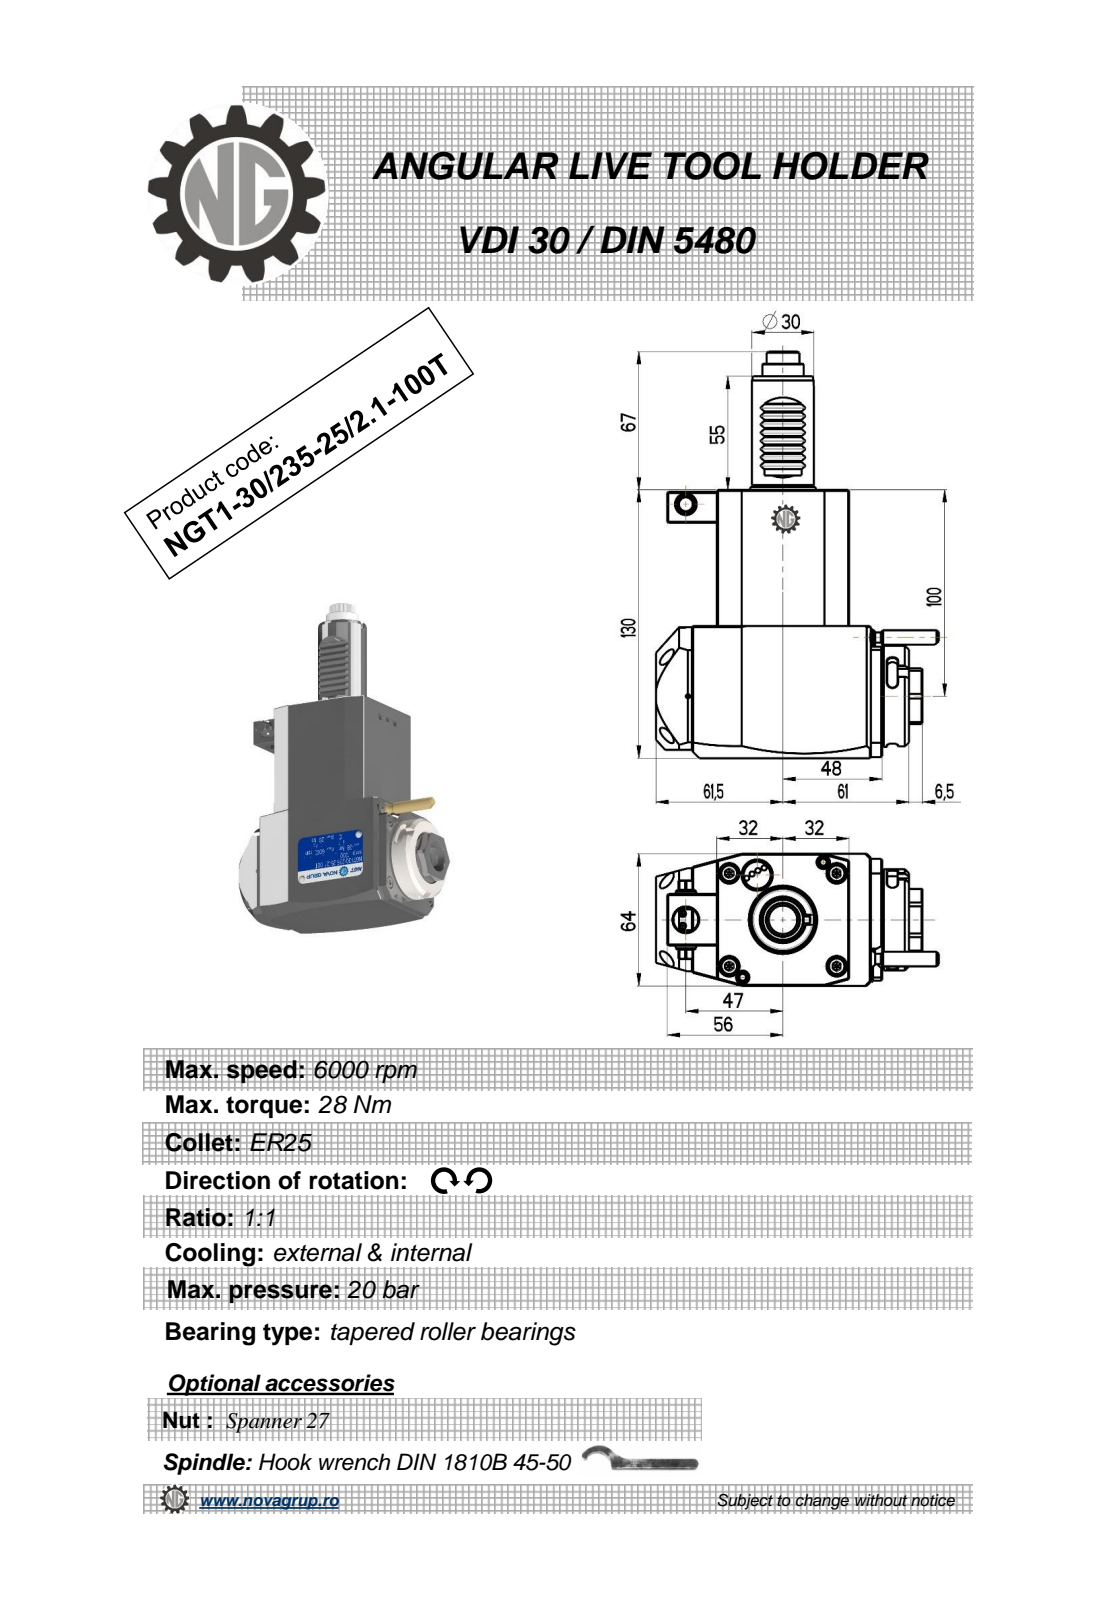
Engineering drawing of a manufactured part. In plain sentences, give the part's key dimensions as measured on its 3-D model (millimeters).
The part is named "NGT1_30_235_25_1_1_100T". Its 3-D file was written by "PRO/ENGINEER BY PARAMETRIC TECHNOLOGY CORPORATION, 2010280 (CONFIG_CONTROL_DESIGN)". It is 1 solid with 427 faces: 186 planar, 153 cylindrical and 88 other. Overall it measures 197 by 136.88 by 64 millimeters. Its volume is 739 925 cubic millimeters and its surface area 62 056 square millimeters. Round holes: 1 of diameter 2.5, 1 of diameter 3, 1 of diameter 9.5, 1 of diameter 12, 1 of diameter 18. Round bosses or shafts: 2 of diameter 8, 1 of diameter 49, 1 of diameter 42, 1 of diameter 30, 1 of diameter 20, 1 of diameter 10, 1 of diameter 7, 1 of diameter 5. Partial cylindrical surfaces (rounded edges, fillets, slot ends): 36 of radius 1.98, 8 of radius 0.3, 6 of radius 2.5, 2 of radius 180, 1 of radius 3.85, 1 of radius 4.25, 1 of radius 4.5, 1 of radius 7.08. The main face-to-face distances are 64, 130, 16, 80, 72.18, 13, 29.5, 93.5, 109.5, 66. The hole center spacings are 34.25, 65.8, 91.5.
